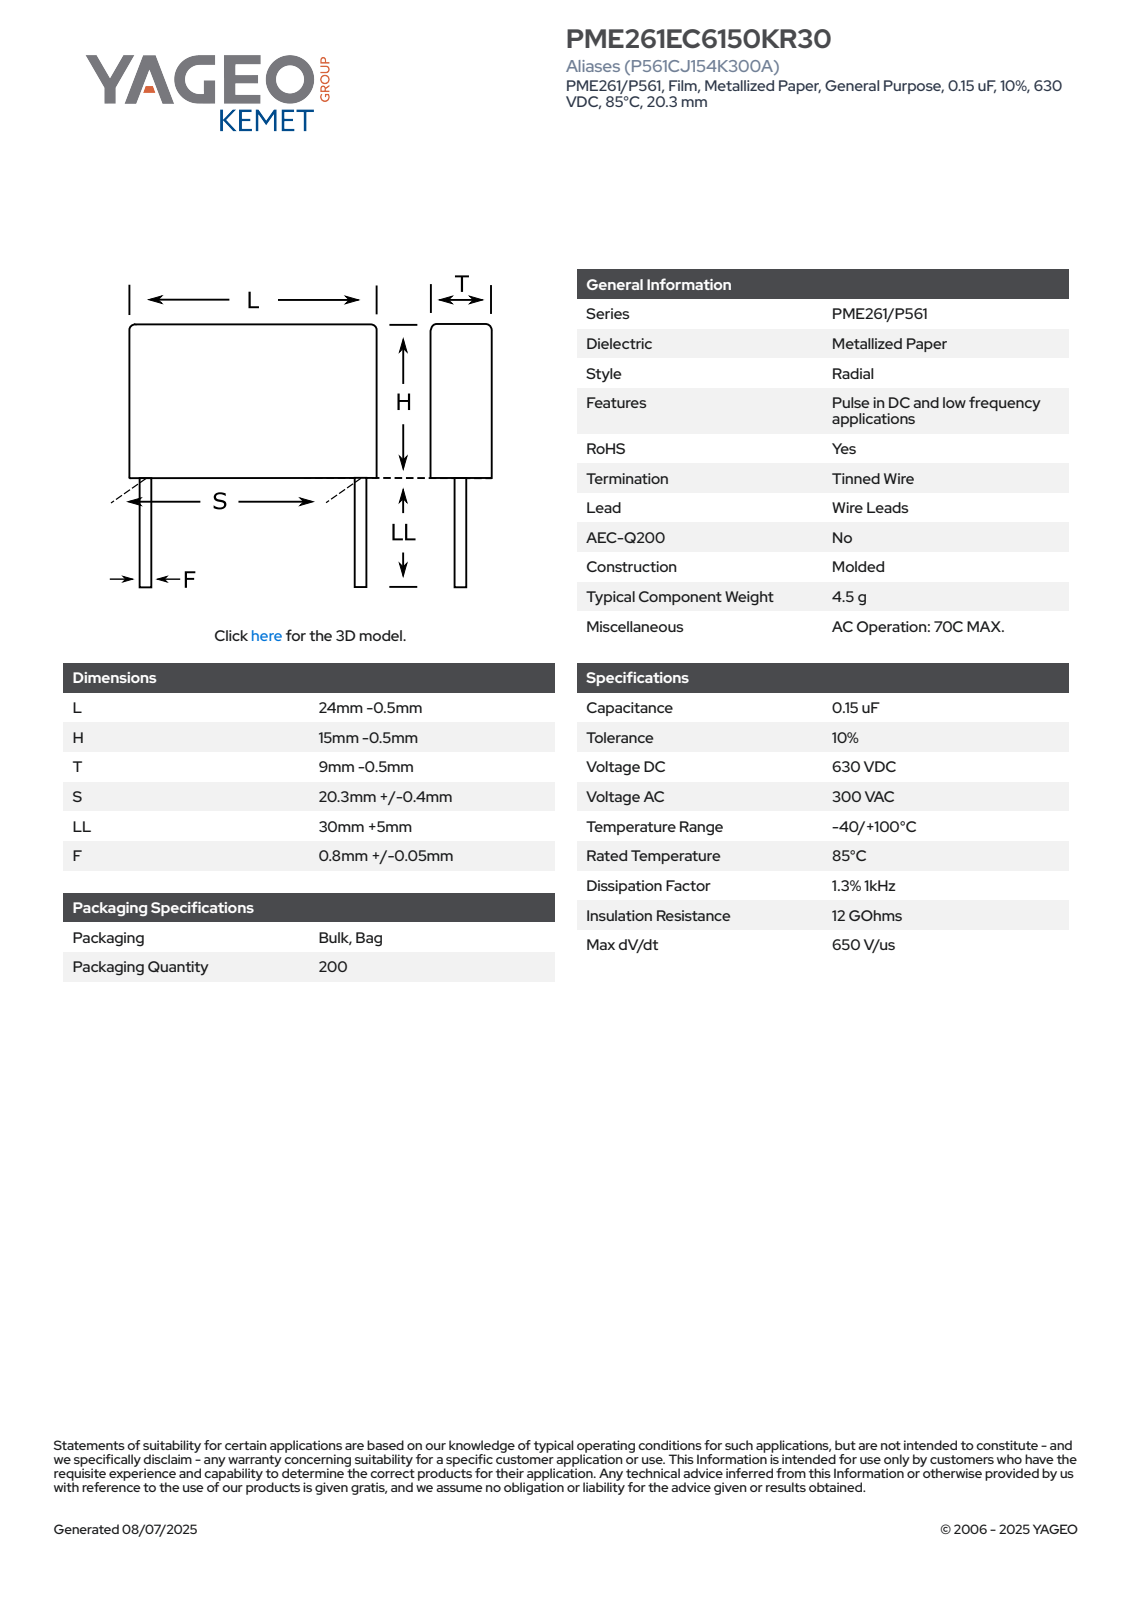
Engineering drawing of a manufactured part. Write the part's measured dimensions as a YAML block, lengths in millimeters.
part_name: "CFR_MOLDED_24X15X9_L23.5H14.5T8.5S20.3LL35F0.85"
step_written_by: "SolidWorks 2014 (AUTOMOTIVE_DESIGN)"
units: millimeters
bodies: {solids: 4, faces: 73, planar: 65, cylindrical: 8, other: 0}
overall_size: [49.5, 23.5, 8.51]
volume: 2933
surface_area: 1527
round_bosses_or_shafts:
  - {diameter: 0.85, count: 2}
partial_cylinders:
  - {radius: 0.5, count: 4}
face_to_face_distances: [8.5, 14.5, 23.5, 8.51, 35, 49.5, 43.19, 8.19, 6.31, 41.08]
